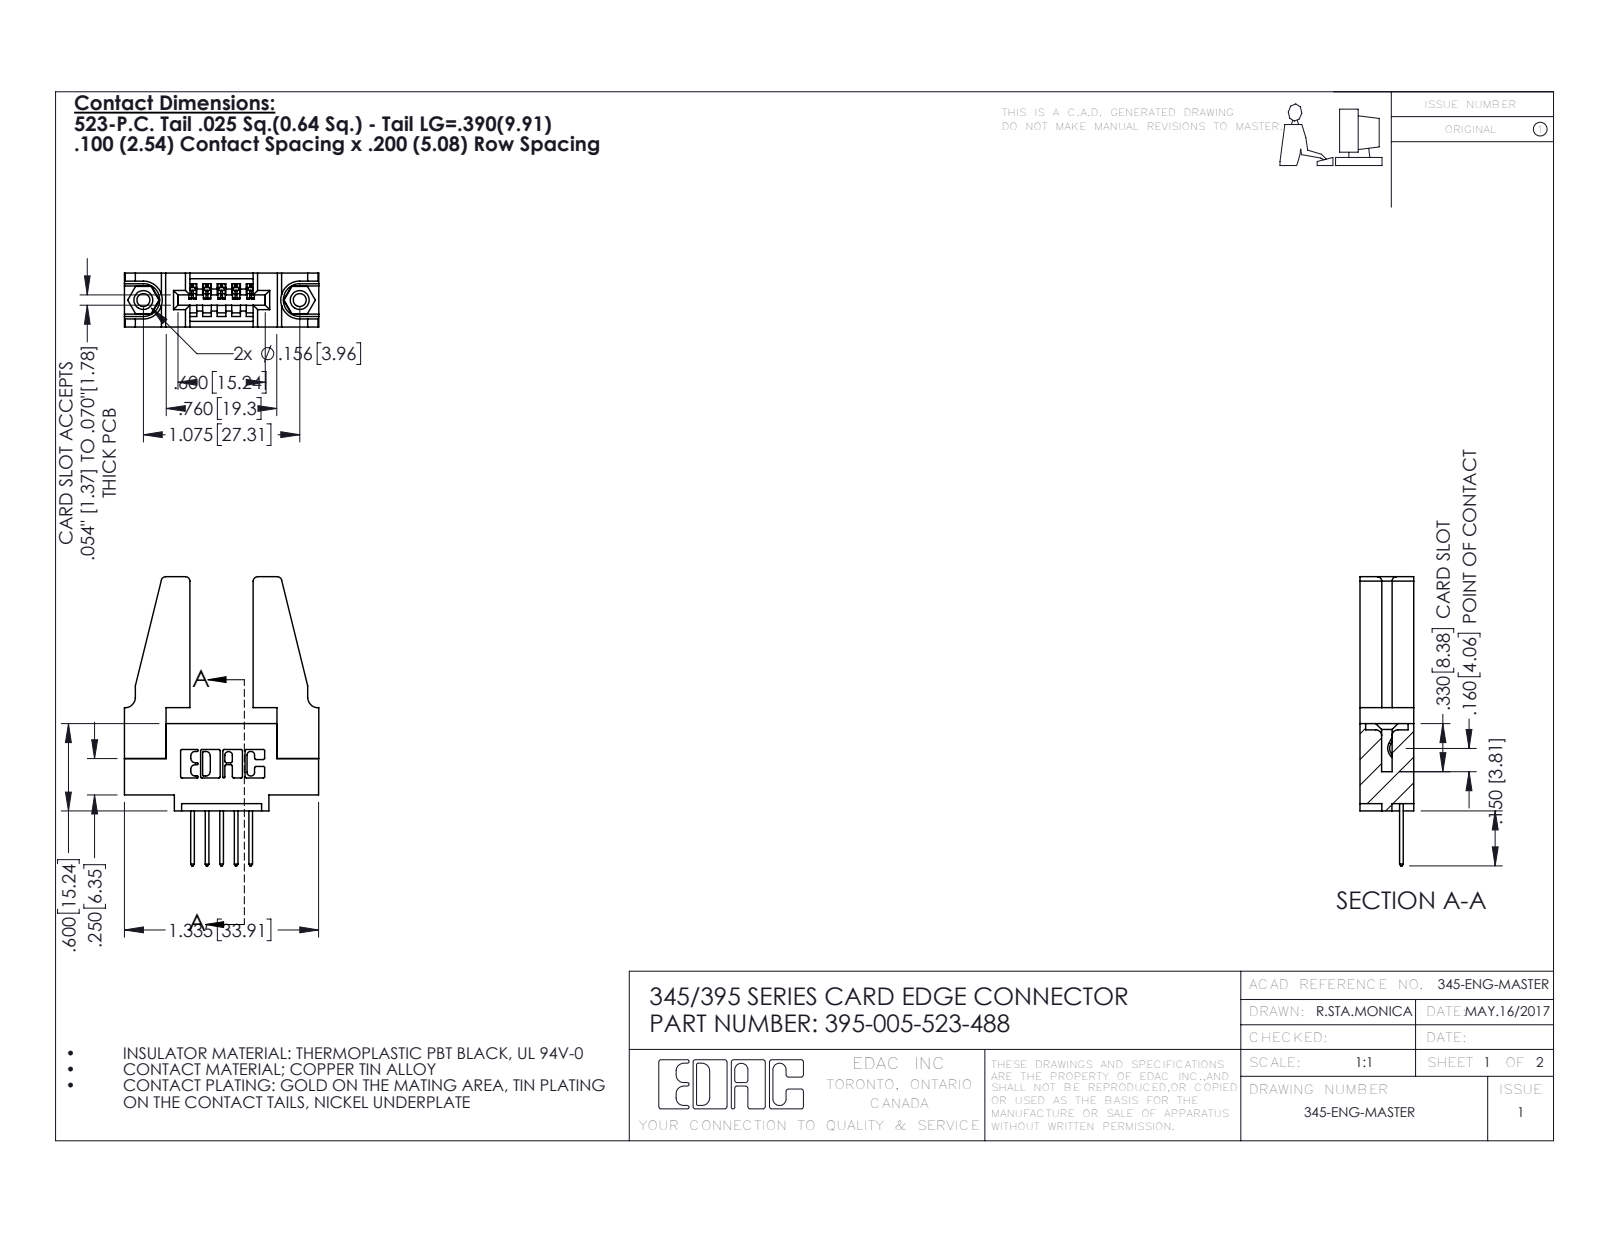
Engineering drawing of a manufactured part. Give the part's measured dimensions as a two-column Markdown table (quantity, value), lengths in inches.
| quantity | value |
| --- | --- |
| part name | 345-292-001_345-293-123; 345-250-001_345-250-001-102; 345 Part_0.110 Offset - 0.156 Dia-TH; 345-220-078_345-220-088 (+1 more) |
| STEP written by | SolidWorks 2016 (CONFIG_CONTROL_DESIGN) |
| units | inches |
| bodies | 10 solids, 544 faces (356 planar, 172 cylindrical, 16 other) |
| overall size | 1.987 × 1.336 × 0.37 |
| volume | 0.372 in³ |
| surface area | 10.07 in² |
| round holes (diameter × count) | 0.089 × 2, 0.125 × 2, 0.156 × 2, 0.064 × 1 |
| round bosses / shafts (diameter × count) | 0.155 × 2 |
| partial cylindrical surfaces (radius × count) | 0.01 × 22, 0.006 × 10, 0.01 × 10, 0.03 × 8, 0.007 × 6, 0.031 × 6, 0.026 × 3, 0.031 × 2 |
| main face-to-face distances | 0.37, 0.072, 0.298, 0.2, 0.148, 0.15, 0.22, 0.077, 0.45, 0.287 |
| hole center spacings | 0.27, 0.847, 1.075 |
